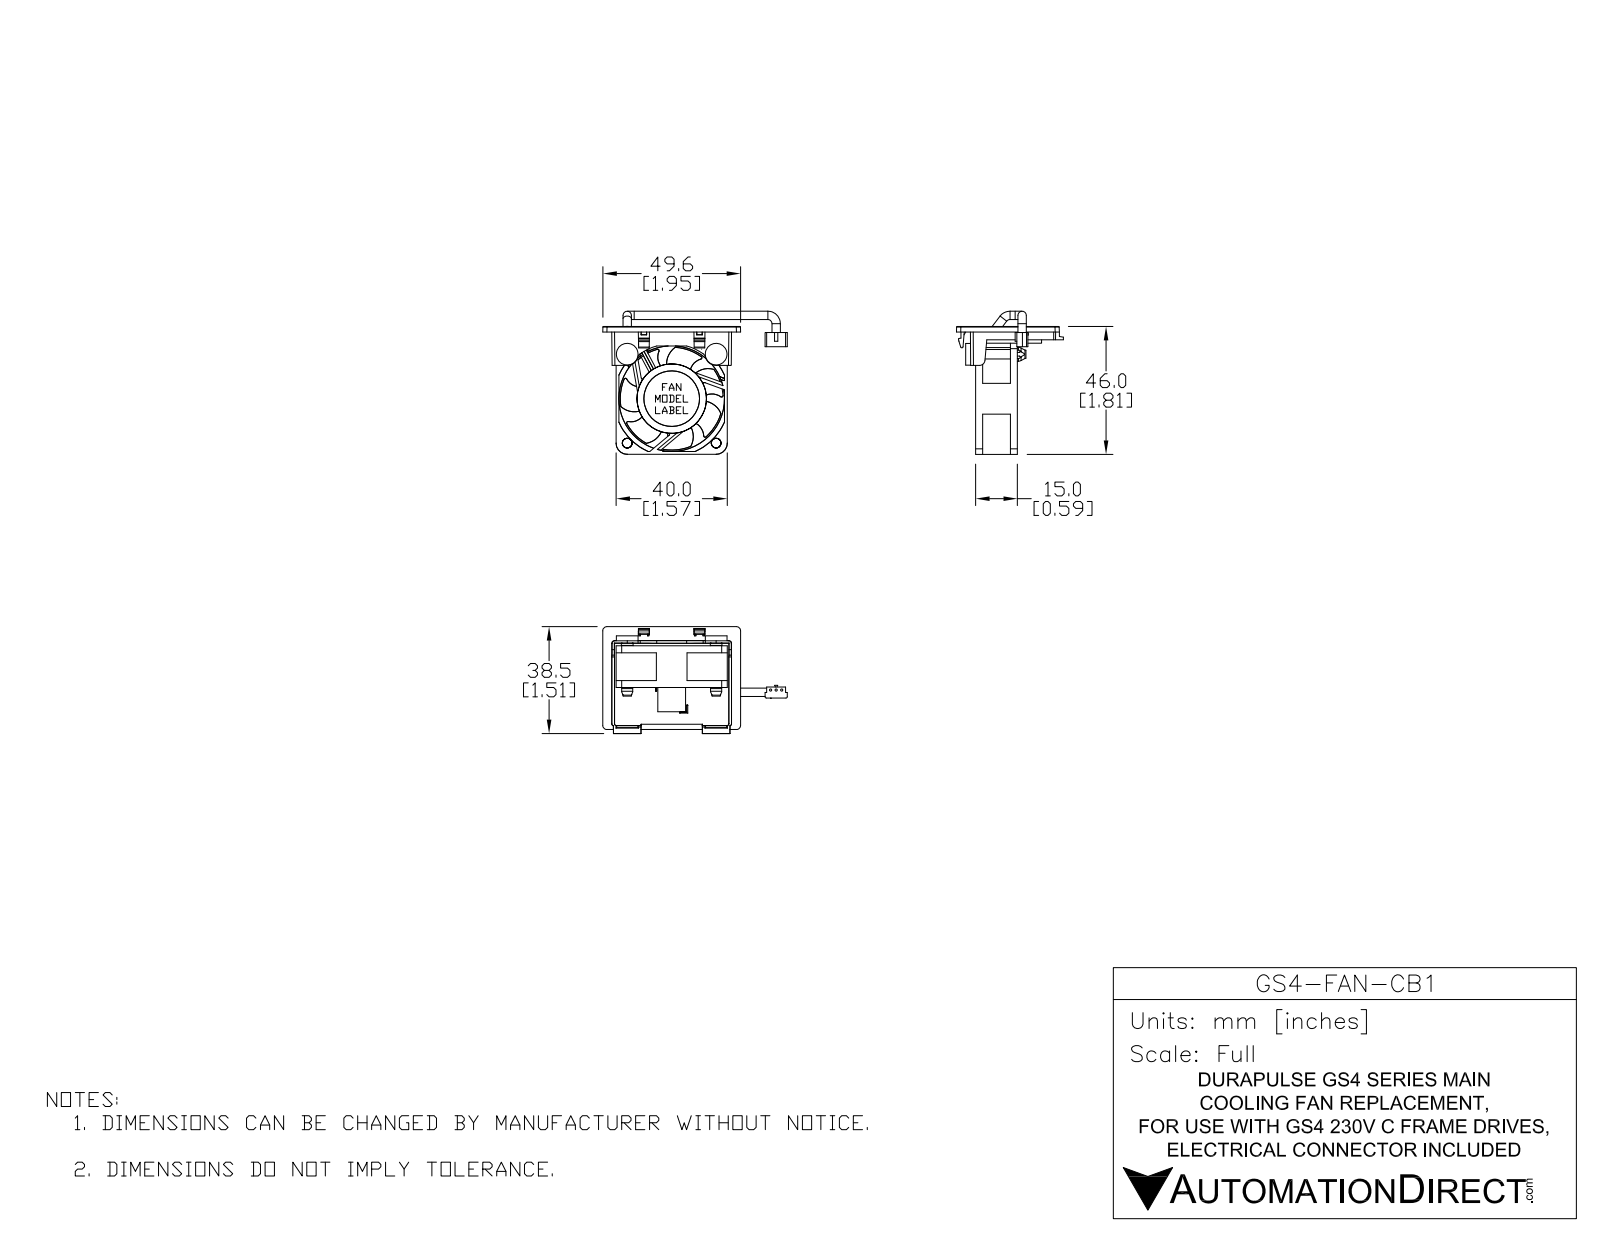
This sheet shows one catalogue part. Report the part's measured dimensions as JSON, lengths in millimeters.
{"part_name": "GS4-FAN-CB1", "step_written_by": "SolidWorks 2015 (AUTOMOTIVE_DESIGN)", "units": "millimeters", "bodies": {"solids": 0, "faces": 252, "planar": 138, "cylindrical": 90, "other": 24}, "overall_size": [68.22, 51.5, 42.19], "round_holes": [[3.5, 2], [7.8, 2]], "round_bosses_or_shafts": [[3, 5], [5, 2], [3.6, 2], [18, 1]], "partial_cylinders_radius": [[0.2, 13], [2, 9], [1.5, 4], [0.5, 2], [0.7, 2], [1, 2], [4, 2], [19.75, 2]], "face_to_face_distances": [1.8, 2.5, 15, 0.7, 1.3, 2, 4, 6, 1, 5.3], "hole_center_spacings": [32, 45.26]}
